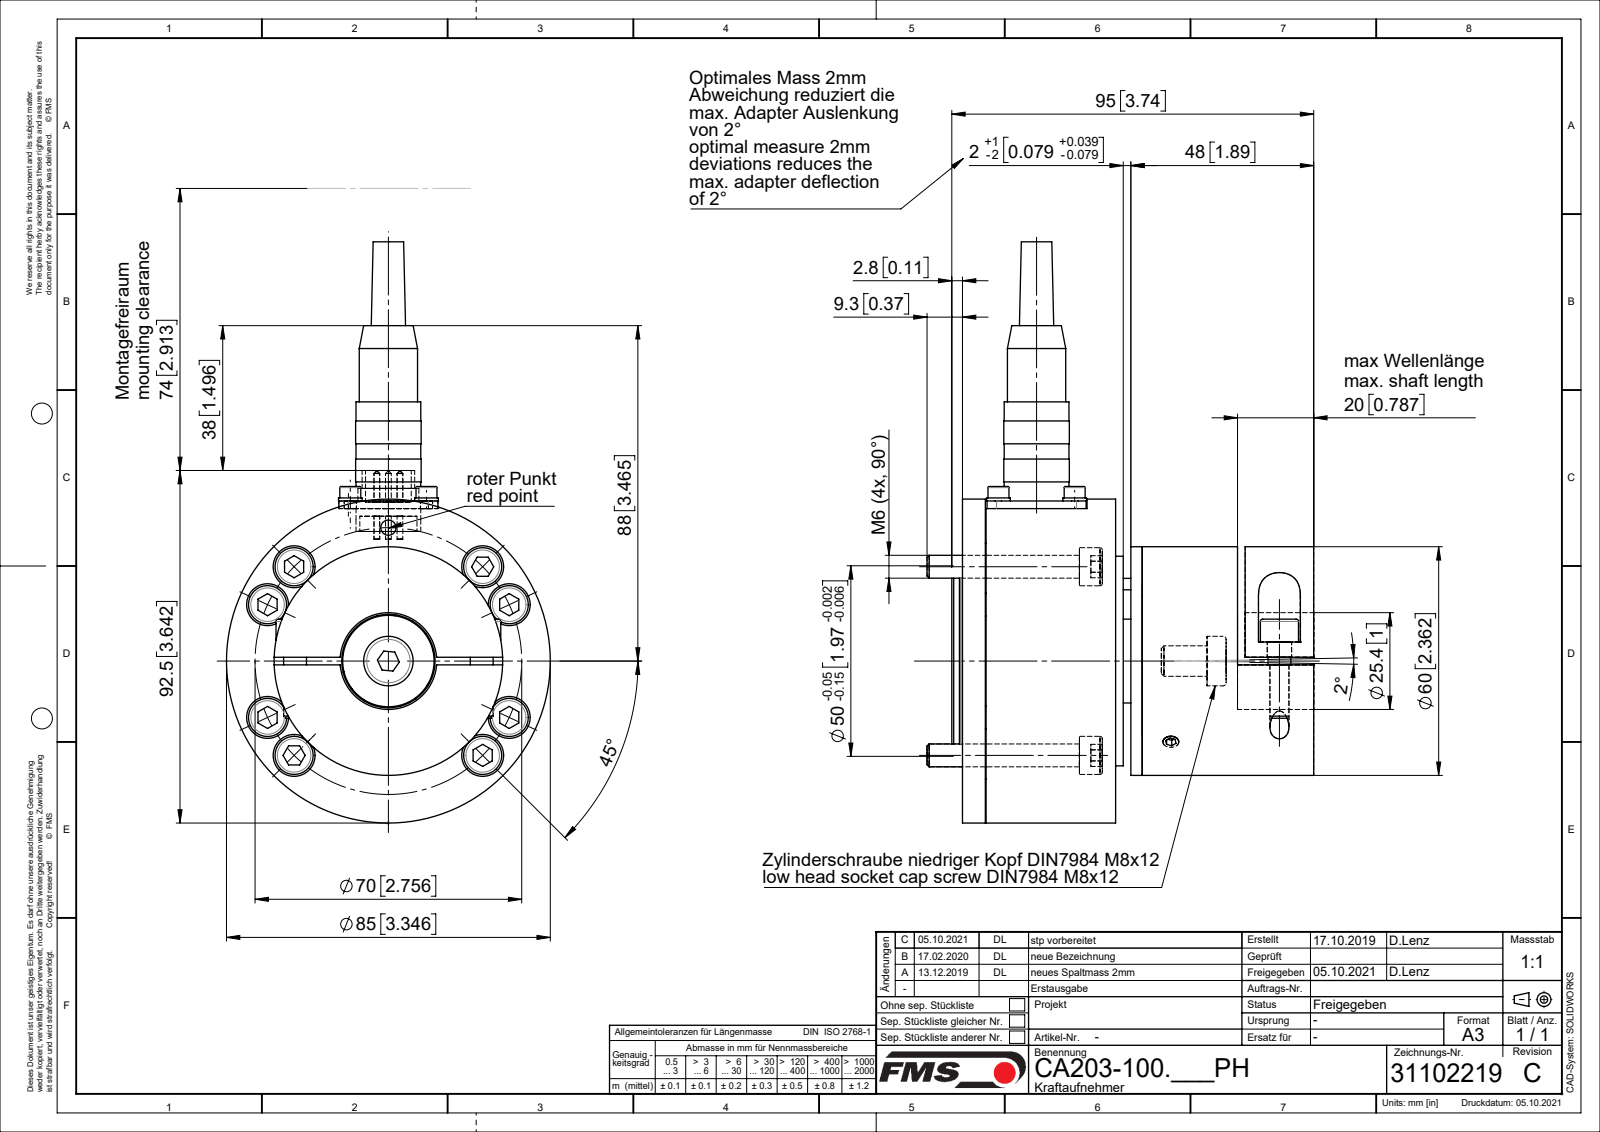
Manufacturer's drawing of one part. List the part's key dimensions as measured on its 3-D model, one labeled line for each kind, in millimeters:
Part name (STEP PRODUCT): Flanschstecker_M14x1_Mini_5pol; Se-Schr DIN7991_M3x8; 31102219_C; 091113-3_stp_01 (+8 more)
STEP written by: SolidWorks 2018 (CONFIG_CONTROL_DESIGN)
Units: millimetres
Bodies: 44 solids, 821 faces (294 planar, 332 cylindrical, 195 other)
Overall size (bounding box): 152.5 × 101.5 × 85
Volume: 302 152 mm³ · Surface area: 109 820 mm²
Round holes (diameter × count): ⌀2.5 ×8, ⌀6.5 ×8, ⌀11 ×8, ⌀5 ×6, ⌀4 ×5, ⌀3.1 ×4, ⌀3.2 ×4, ⌀3.6 ×4, ⌀7 ×4, ⌀6.4 ×2, ⌀3 ×1, ⌀4.2 ×1
Round bosses / shafts (diameter × count): ⌀6 ×11, ⌀10 ×10, ⌀3 ×8, ⌀1.5 ×5, ⌀6.2 ×4, ⌀5.7 ×4, ⌀5.5 ×4, ⌀85 ×1
Partial cylindrical surfaces — rounded edges, fillets, slot ends (radius × count): R2.5 ×4, R5 ×2, R5.5 ×2
Main face-to-face distances: 2, 41, 30, 6, 45, 10, 50, 34, 3, 12
Hole centre spacings: 35, 20, 24.78, 25.2, 32.8, 51.14, 56.46, 28.28
